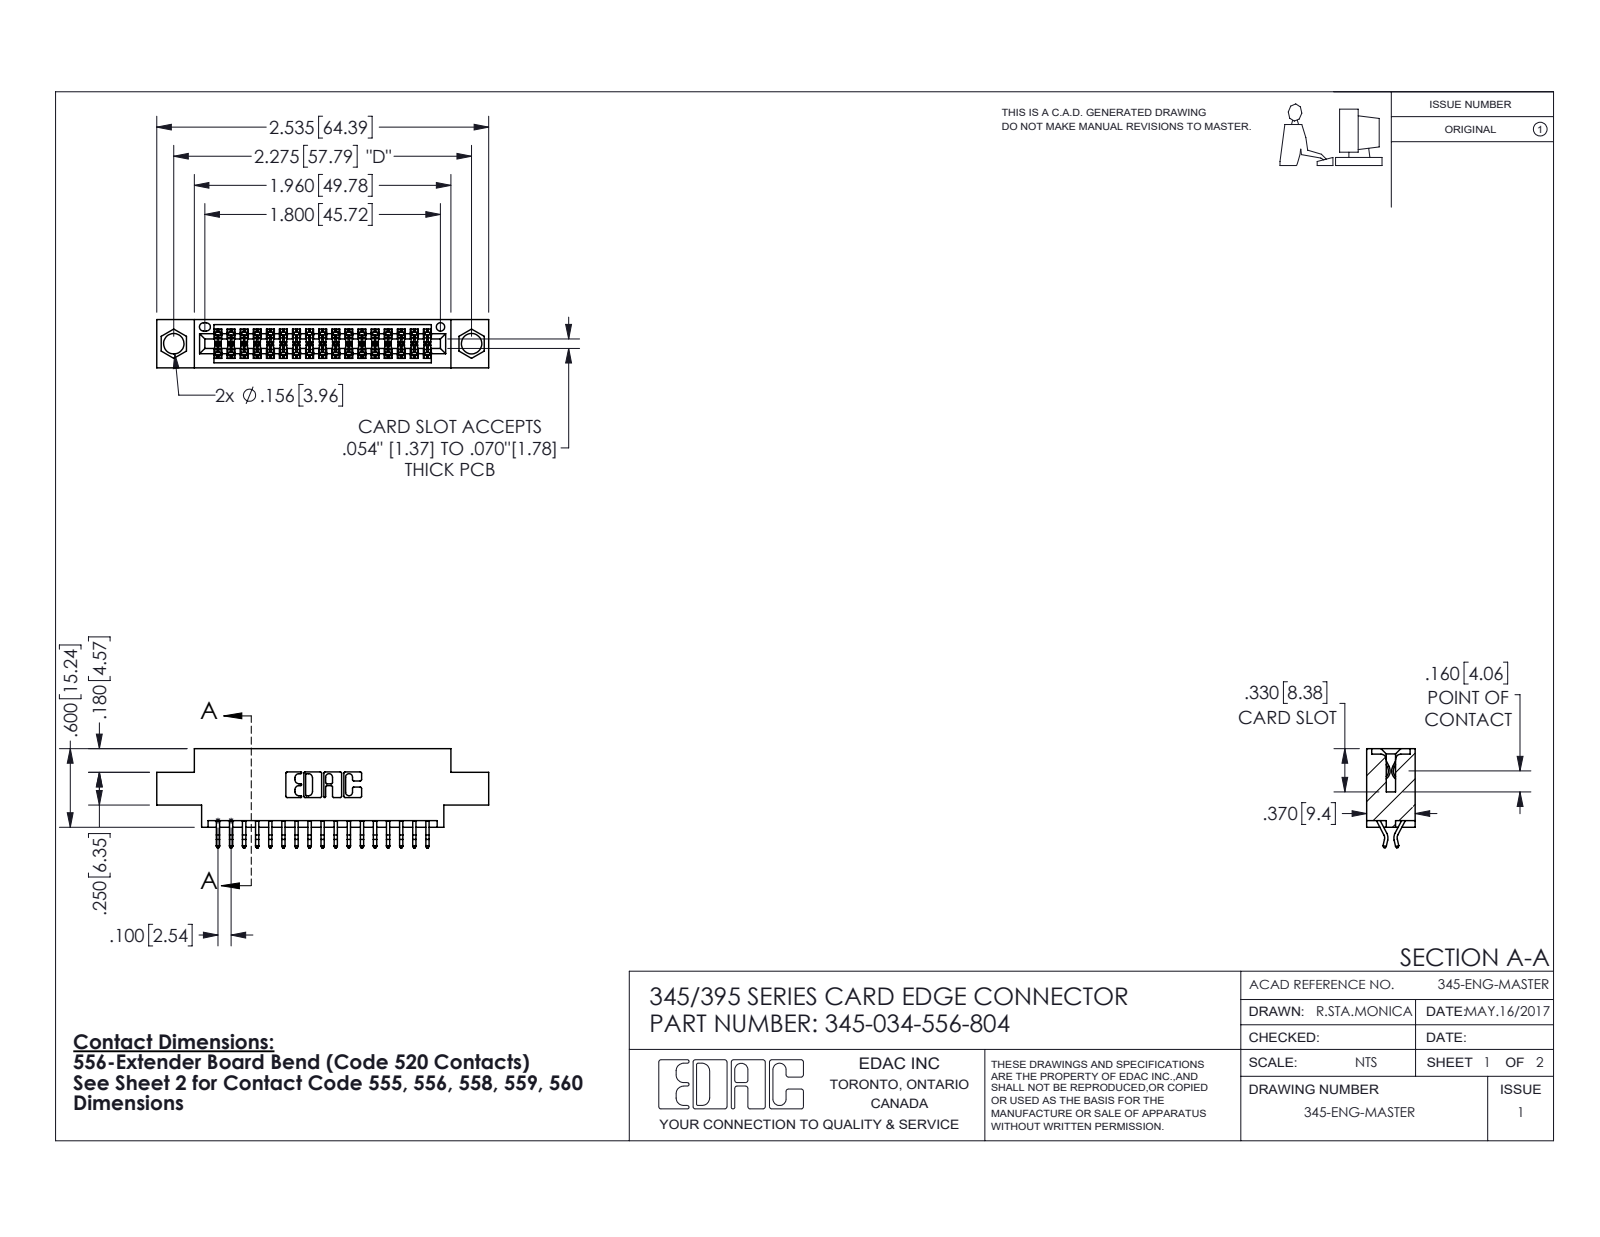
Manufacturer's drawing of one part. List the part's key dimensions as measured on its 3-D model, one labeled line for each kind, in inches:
Part name (STEP PRODUCT): 345-292-001_556 Tail; 345 Part_0.170 Offset - 0.156 Dia-TI; 345-034-556-804
STEP written by: SolidWorks 2020 (CONFIG_CONTROL_DESIGN)
Units: inches
Bodies: 35 solids, 2048 faces (1356 planar, 692 cylindrical, 0 other)
Overall size (bounding box): 2.535 × 0.757 × 0.37
Volume: 0.354 in³ · Surface area: 12.49 in²
Round holes (diameter × count): ⌀0.156 ×2, ⌀0.064 ×1
Partial cylindrical surfaces — rounded edges, fillets, slot ends (radius × count): R0.006 ×68, R0.01 ×22, R0.007 ×6, R0.031 ×6, R0.026 ×3, R0.01 ×2, R0.014 ×2, R0.019 ×2
Main face-to-face distances: 0.072, 0.298, 0.37, 0.2, 0.025, 0.098, 0.272, 0.225, 0.175, 0.1
Hole centre spacings: 0.27, 2.041, 2.275
